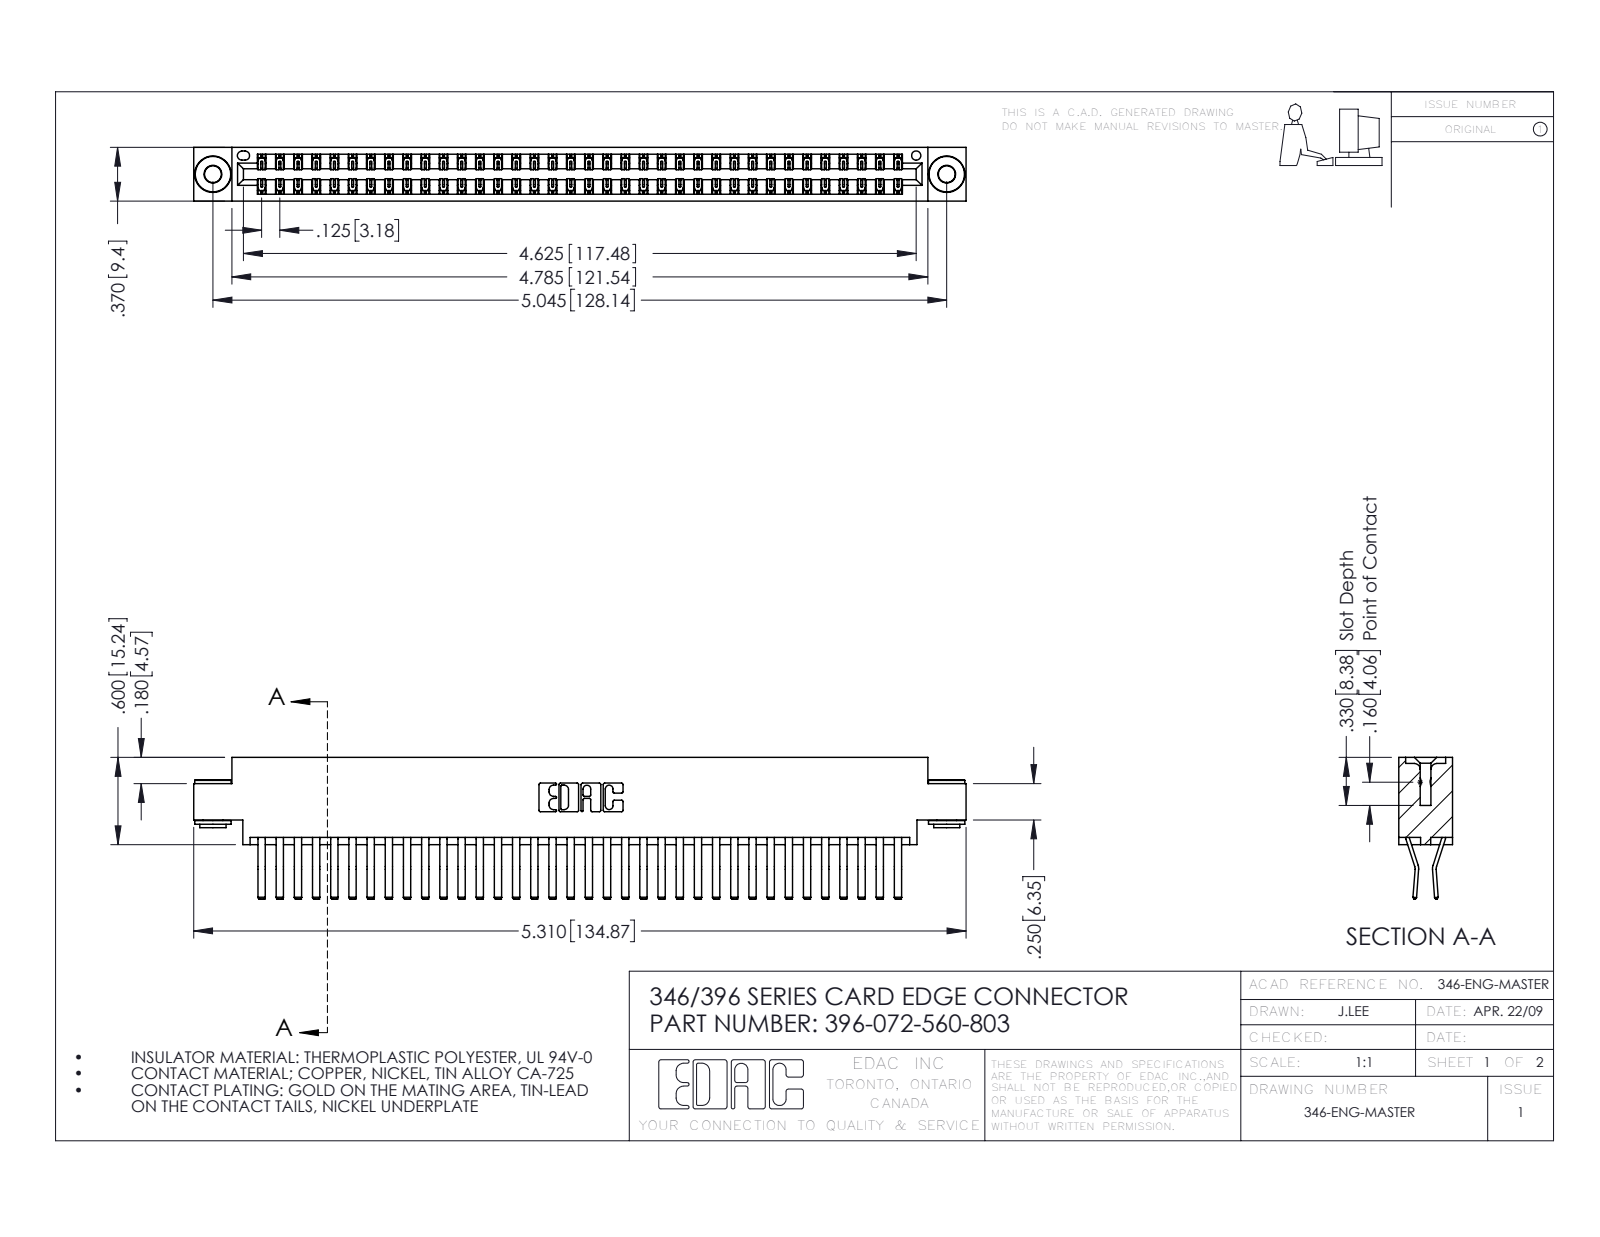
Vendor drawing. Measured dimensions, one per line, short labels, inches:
name: 345-250-002_345-250-002-102; 346 Part_0.170 Offset - 0.156 Dia-TH; 345-292-001_560 Tail; 396-072-560-803
written by: SolidWorks 2016 (CONFIG_CONTROL_DESIGN)
unit: in
bodies: 75 solids, 4052 faces (2610 planar, 1434 cylindrical, 8 other)
size: 5.31 × 0.975 × 0.37
volume: 0.82 in³; area: 31.06 in²
holes: 2× ⌀0.116, 2× ⌀0.156, 1× ⌀0.064
bosses: 2× ⌀0.25, 2× ⌀0.18, 2× ⌀0.136
rounds: 108× R0.006, 22× R0.01, 6× R0.007, 6× R0.031, 3× R0.026, 2× R0.01, 2× R0.014, 2× R0.022
face distances: 0.048, 0.322, 0.37, 0.025, 0.25, 0.275, 0.072, 0.298, 0.148, 0.222
hole spacings: 0.246, 4.836, 5.045
